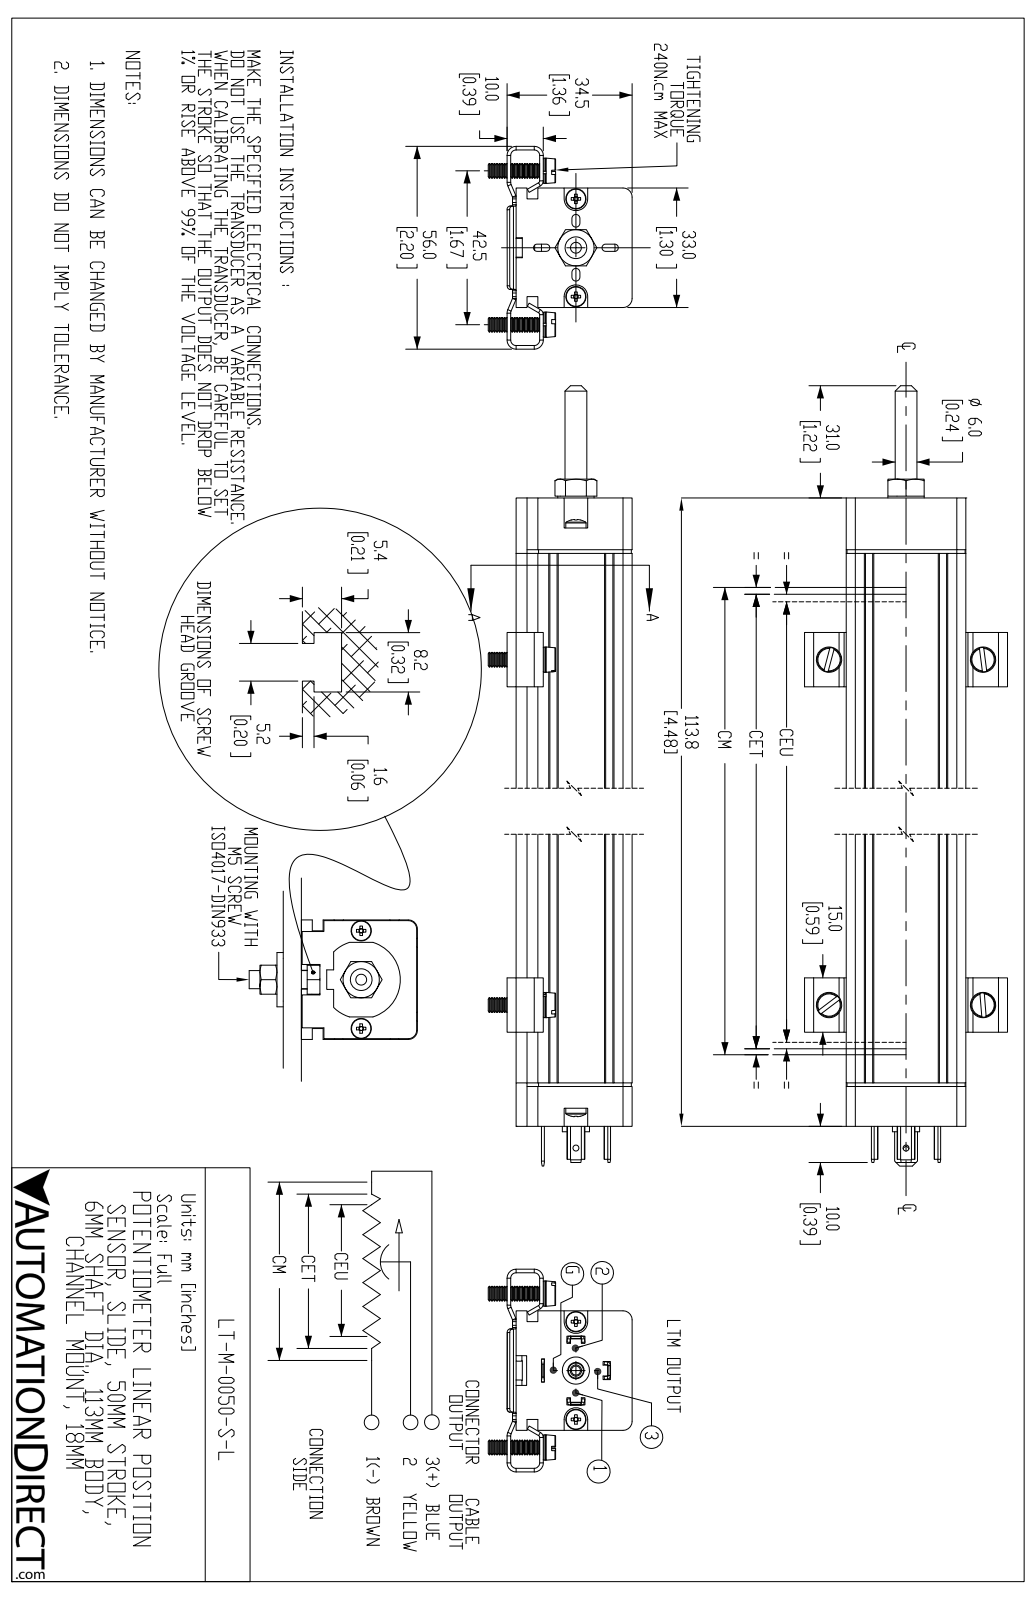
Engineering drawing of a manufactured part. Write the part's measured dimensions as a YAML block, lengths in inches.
part_name: "LT-M-0050-S-L"
step_written_by: "SolidWorks 2019 (AUTOMOTIVE_DESIGN)"
units: inches
bodies: {solids: 21, faces: 1620, planar: 696, cylindrical: 356, other: 568}
overall_size: [6.828, 2.205, 1.563]
volume: 7.187
surface_area: 58.36
round_holes:
  - {diameter: 0.142, count: 4}
  - {diameter: 0.059, count: 2}
  - {diameter: 0.065, count: 2}
  - {diameter: 0.108, count: 2}
  - {diameter: 0.134, count: 2}
  - {diameter: 0.169, count: 2}
  - {diameter: 0.063, count: 1}
  - {diameter: 0.098, count: 1}
  - {diameter: 0.118, count: 1}
  - {diameter: 0.163, count: 1}
  - {diameter: 0.197, count: 1}
  - {diameter: 0.276, count: 1}
round_bosses_or_shafts:
  - {diameter: 0.274, count: 4}
  - {diameter: 0.157, count: 4}
  - {diameter: 0.22, count: 2}
  - {diameter: 0.118, count: 2}
  - {diameter: 0.295, count: 1}
  - {diameter: 0.236, count: 1}
  - {diameter: 0.177, count: 1}
  - {diameter: 0.173, count: 1}
partial_cylinders:
  - {radius: 0.039, count: 34}
  - {radius: 0.098, count: 12}
  - {radius: 0.059, count: 10}
  - {radius: 0.085, count: 8}
  - {radius: 0.033, count: 6}
  - {radius: 0.043, count: 4}
  - {radius: 0.024, count: 2}
  - {radius: 0.063, count: 2}
face_to_face_distances: [0.039, 1.299, 1.26, 0.118, 0.059, 0.02, 0.295, 1.287, 0.213, 0.335]
hole_center_spacings: [0.484, 0.531, 1.359, 1.663, 1.673, 1.766, 1.78, 1.843]
